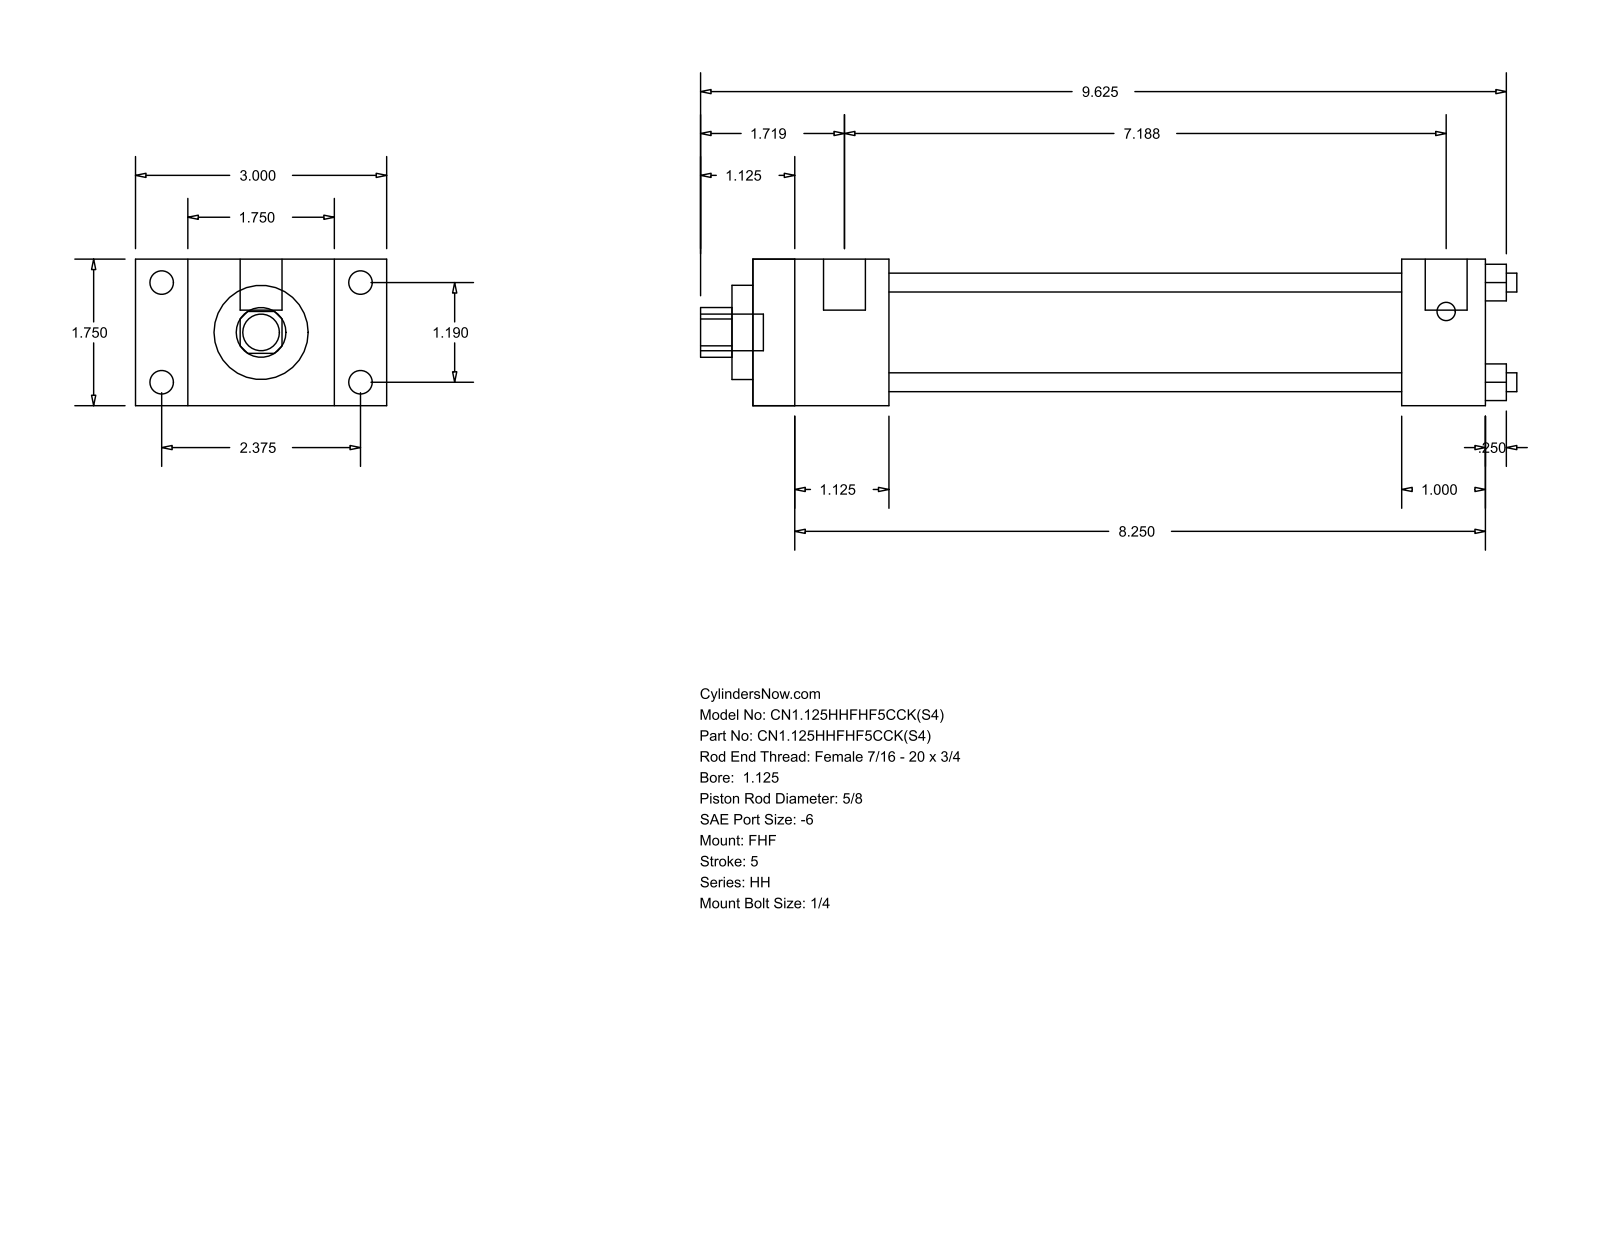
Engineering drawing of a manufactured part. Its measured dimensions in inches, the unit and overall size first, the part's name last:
Units: inches
Overall size (bounding box): 9.75 × 3 × 1.75
Round holes (diameter × count): ⌀0.225 ×4, ⌀0.625 ×1, ⌀1.125 ×1, ⌀1.375 ×1
Round bosses / shafts (diameter × count): ⌀0.281 ×4, ⌀0.219 ×4, ⌀0.5 ×2, ⌀0.437 ×1
Partial cylindrical surfaces — rounded edges, fillets, slot ends (radius × count): R0.297 ×1
Main face-to-face distances: 1.75, 0.625, 2.375, 1.625, 3, 8.75, 7.125, 7.75, 6.125, 1
Hole centre spacings: 0.841, 1.19, 1.683
Bodies: 0 solids, 88 faces (60 planar, 28 cylindrical, 0 other)
Part name (STEP PRODUCT): HH_FHF__0112_0.625
STEP written by: GSSL Pune (CONFIG_CONTROL_DESIGN)
